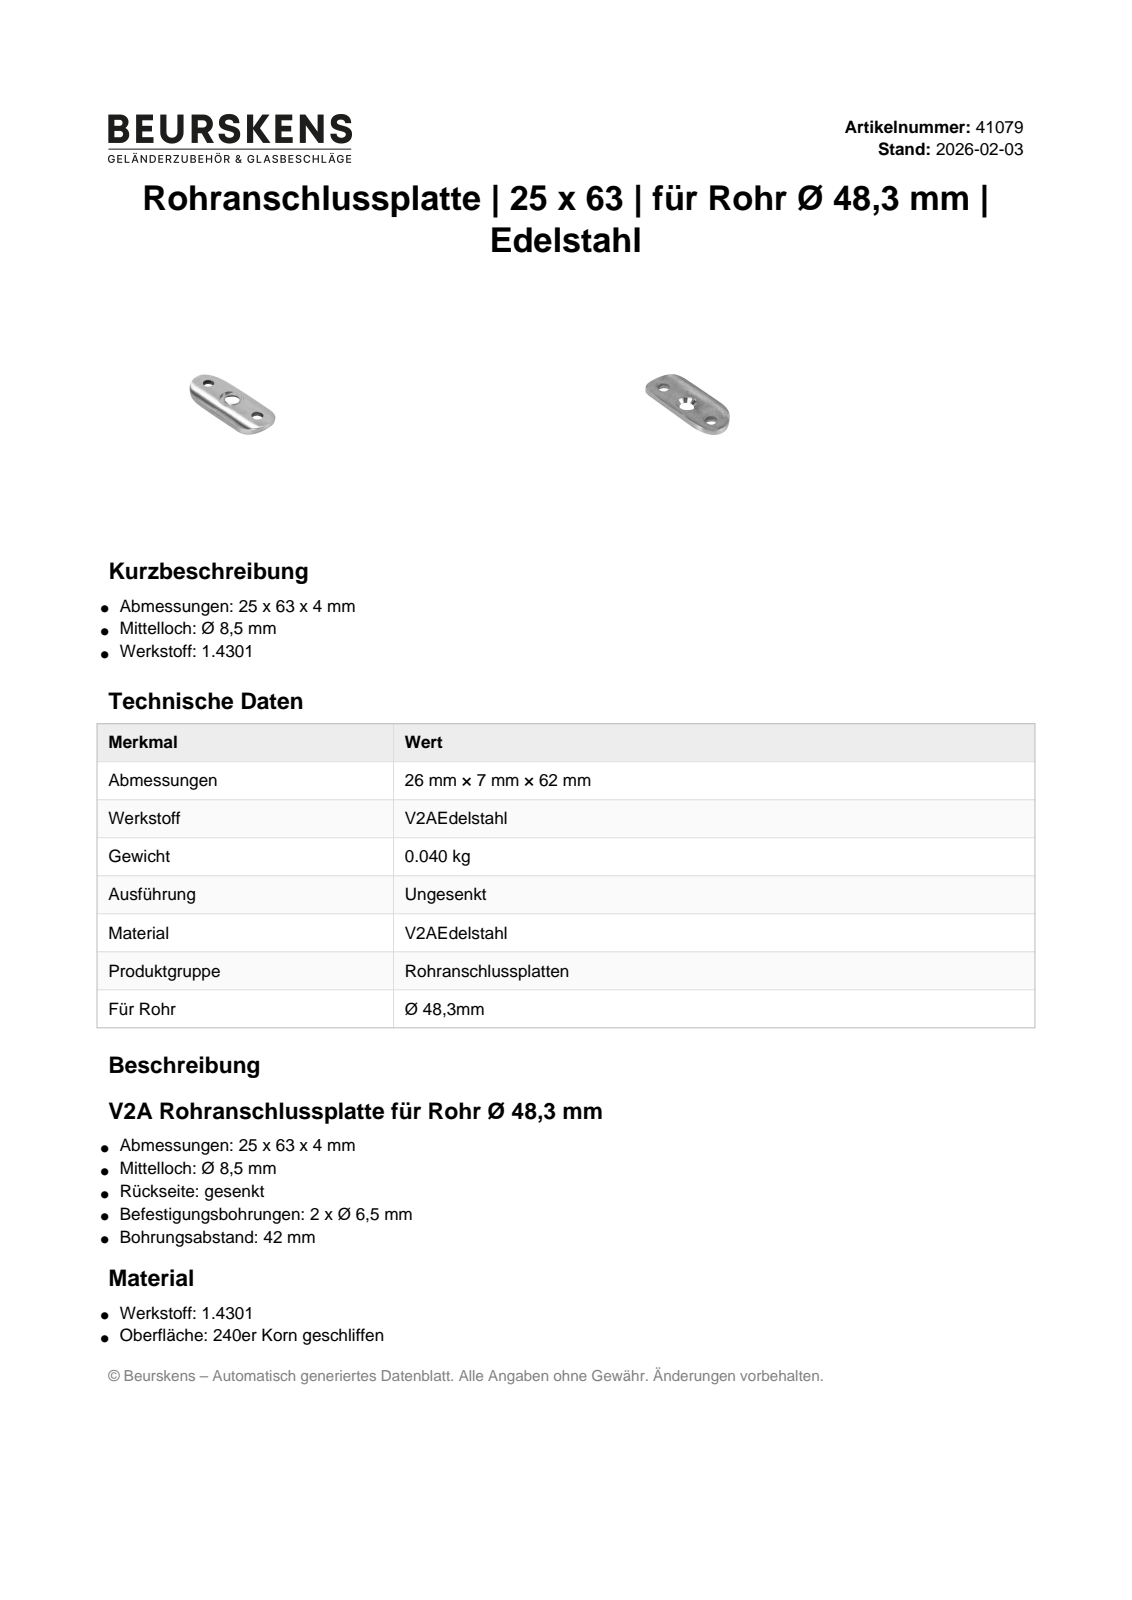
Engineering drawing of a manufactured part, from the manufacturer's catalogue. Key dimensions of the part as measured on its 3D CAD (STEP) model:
Part name (STEP PRODUCT): 41079
STEP written by: Autodesk Inventor 2022 (AUTOMOTIVE_DESIGN)
Units: millimetres
Bodies: 1 solid, 15 faces (3 planar, 7 cylindrical, 5 other)
Overall size (bounding box): 65 × 27.86 × 7.17
Volume: 5 754 mm³ · Surface area: 3 878 mm²
Round holes (diameter × count): ⌀6.5 ×2, ⌀8.5 ×1, ⌀14.2 ×1
Partial cylindrical surfaces — rounded edges, fillets, slot ends (radius × count): R24.1 ×1, R28.1 ×1
Hole centre spacings: 21, 42
